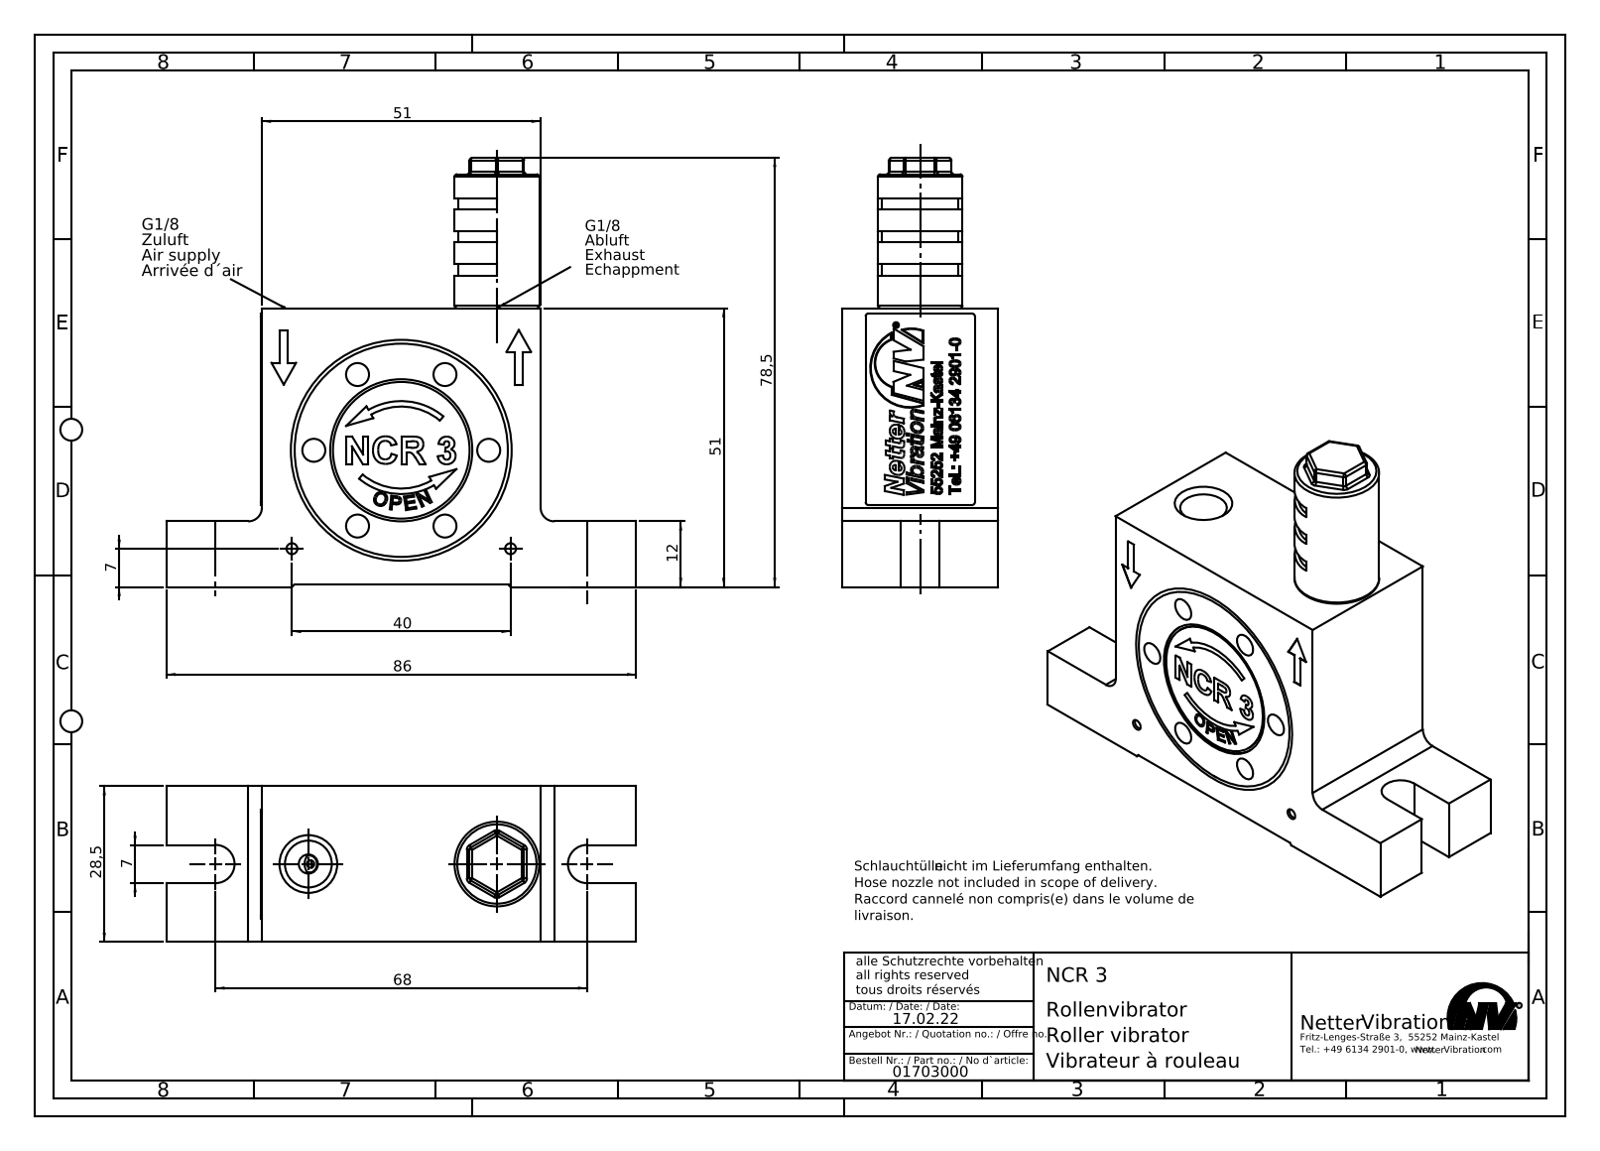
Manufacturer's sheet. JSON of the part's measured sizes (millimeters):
{"part_name": "NCR 3 Rollenvibrator #01703000", "step_written_by": "SolidWorks 2015 (AUTOMOTIVE_DESIGN)", "units": "millimeters", "bodies": {"solids": 2, "faces": 528, "planar": 301, "cylindrical": 81, "other": 146}, "overall_size": [86, 78.5, 29], "volume_mm3": 88564, "surface_area_mm2": 16769, "round_holes": [[4.2, 6], [8.57, 3], [2, 2], [26, 1]], "round_bosses_or_shafts": [[25, 1], [15.5, 1], [9.73, 1]], "partial_cylinders_radius": [[0.5, 22], [2.5, 2], [3.5, 2], [7, 1], [19.5, 1]], "face_to_face_distances": [28.5, 51, 28.75, 0.4, 50.6, 28.9, 28.65, 12, 51.2, 11.6], "hole_center_spacings": [16, 27.71, 12.87, 18.93, 27.24, 27.72, 28.38, 32.01]}
